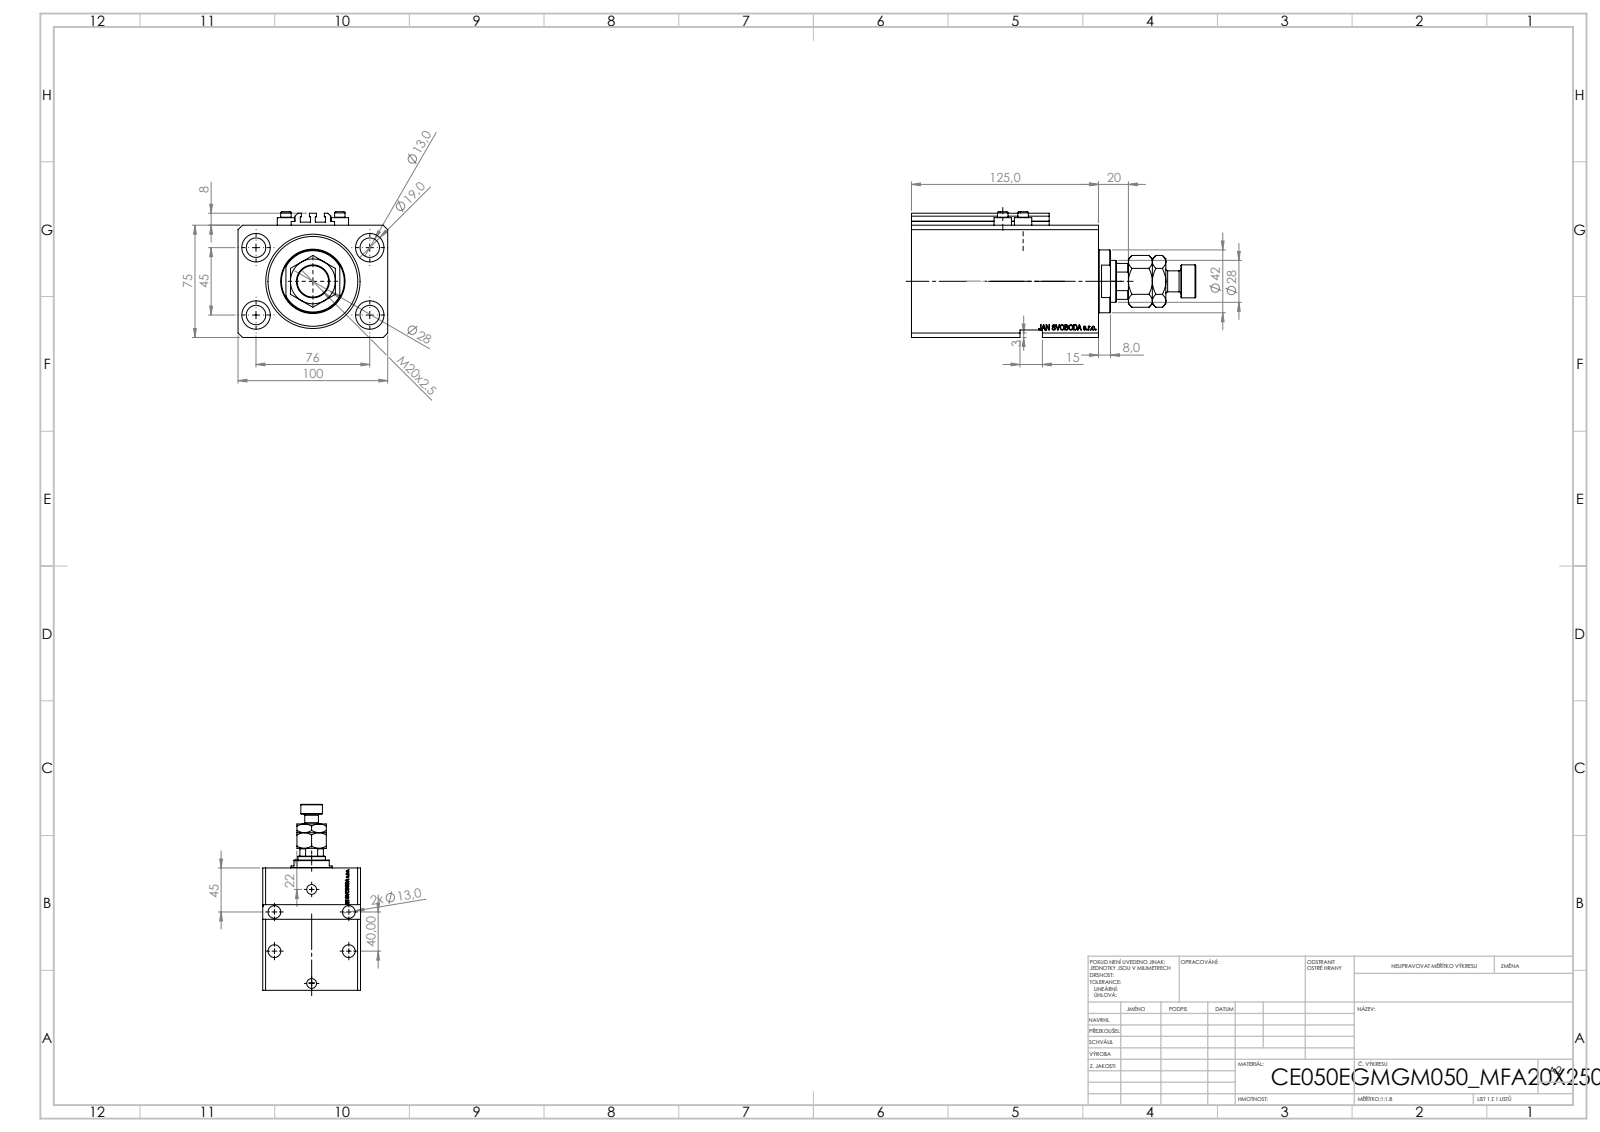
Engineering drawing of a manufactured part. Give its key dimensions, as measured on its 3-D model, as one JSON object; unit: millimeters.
{"part_name": "ALLEN BOLT V250CE; V250CE_C_VCP; MFA; V250CE_E_Body (+1 more)", "step_written_by": "SolidWorks 2019 (CONFIG_CONTROL_DESIGN)", "units": "millimeters", "bodies": {"solids": 9, "faces": 1160, "planar": 551, "cylindrical": 150, "other": 459}, "overall_size": [190, 100, 84], "volume_mm3": 793447, "surface_area_mm2": 155939, "round_holes": [[13, 8], [1.25, 4], [4, 4], [19, 4], [10, 2], [13.16, 2], [20, 2], [18.5, 1], [28, 1], [50, 1], [63, 1]], "round_bosses_or_shafts": [[11.6, 4], [7, 4], [42, 1], [22, 1], [14, 1]], "partial_cylinders_radius": [[0.2, 10], [13.5, 1]], "face_to_face_distances": [75, 100, 20, 125, 11.9, 113.1, 105, 93.1, 70, 3], "hole_center_spacings": [44.16, 76, 13.6, 20.72, 27.59, 29, 33.62, 36]}
